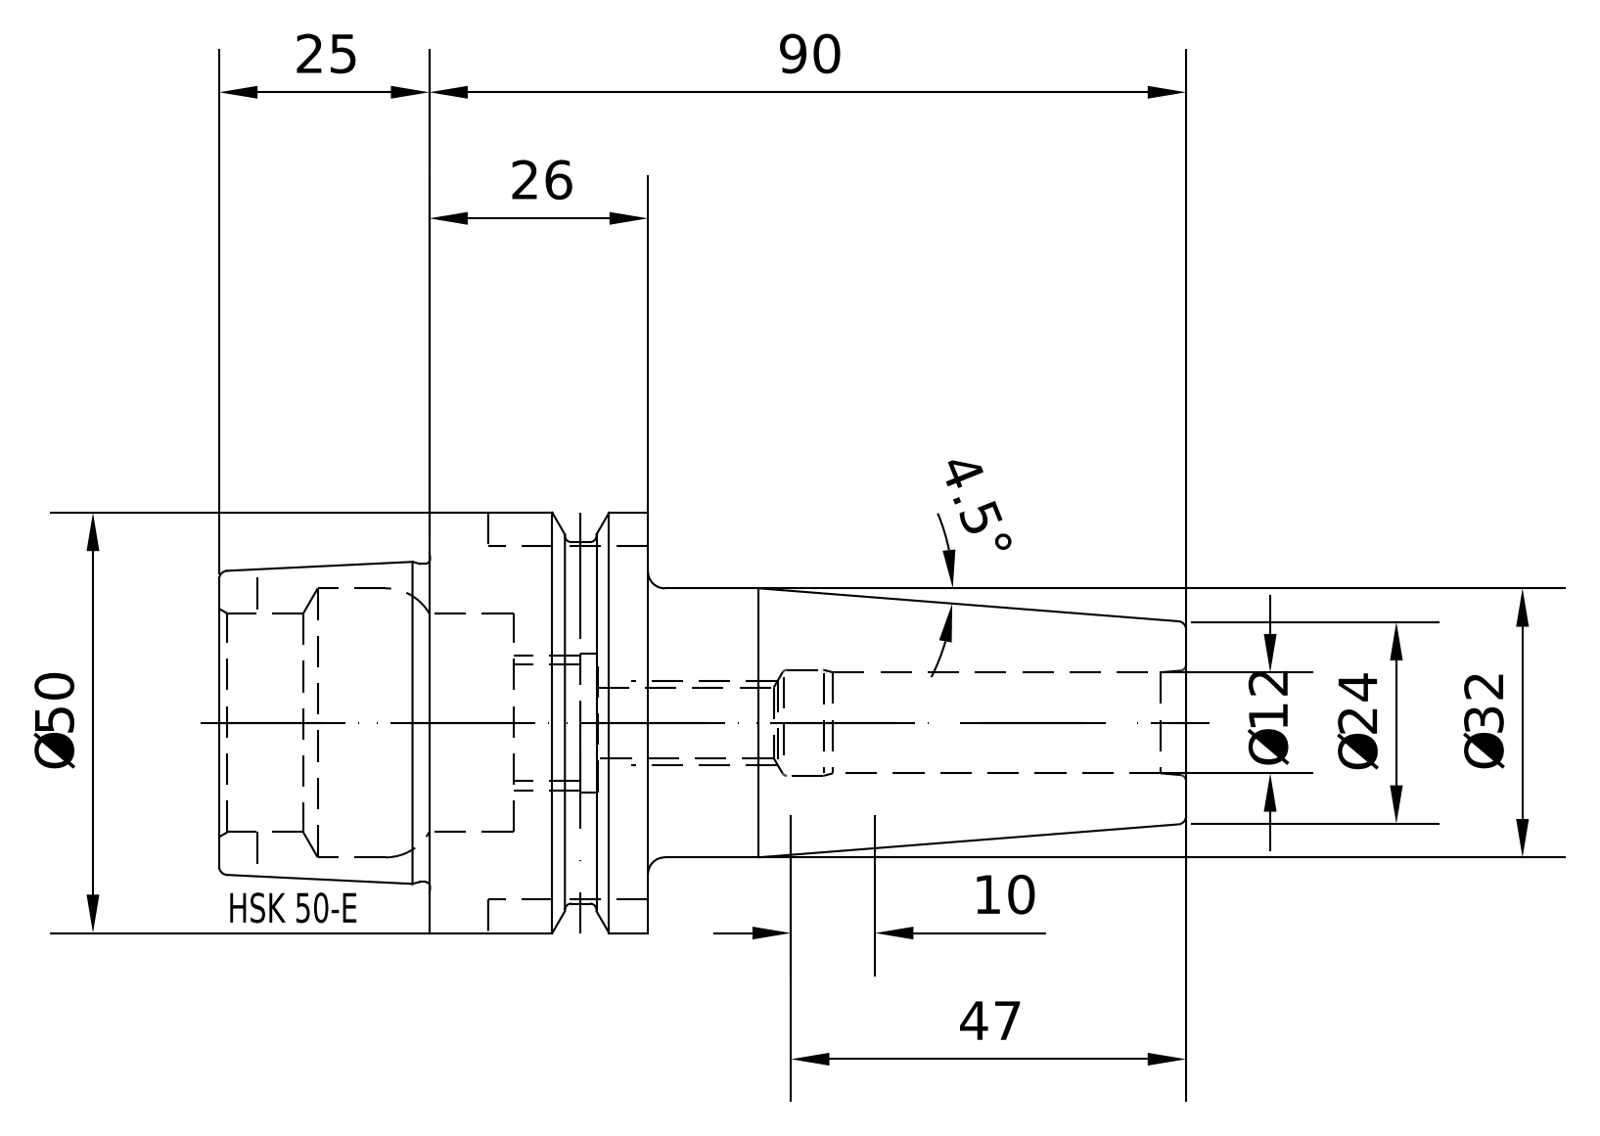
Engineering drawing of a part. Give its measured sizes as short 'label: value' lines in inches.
name: E50-140-12
written by: PRO/ENGINEER BY PARAMETRIC TECHNOLOGY CORPORATION, 2010430 (CONFIG_CONTROL_DESIGN)
unit: in
bodies: 1 solid, 79 faces (9 planar, 24 cylindrical, 46 other)
size: 4.524 × 1.969 × 1.969
volume: 5.401 in³; area: 34.42 in²
holes: 1× ⌀0.472, 1× ⌀0.551, 1× ⌀0.643, 1× ⌀0.65, 1× ⌀1.025, 1× ⌀1.263
bosses: 1× ⌀1.969, 1× ⌀1.691, 1× ⌀1.493, 1× ⌀1.26
face distances: 1.022, 0.98, 2.002, 4.524, 3.543, 2.522, 1.372, 0.392, 0.63, 3.152
